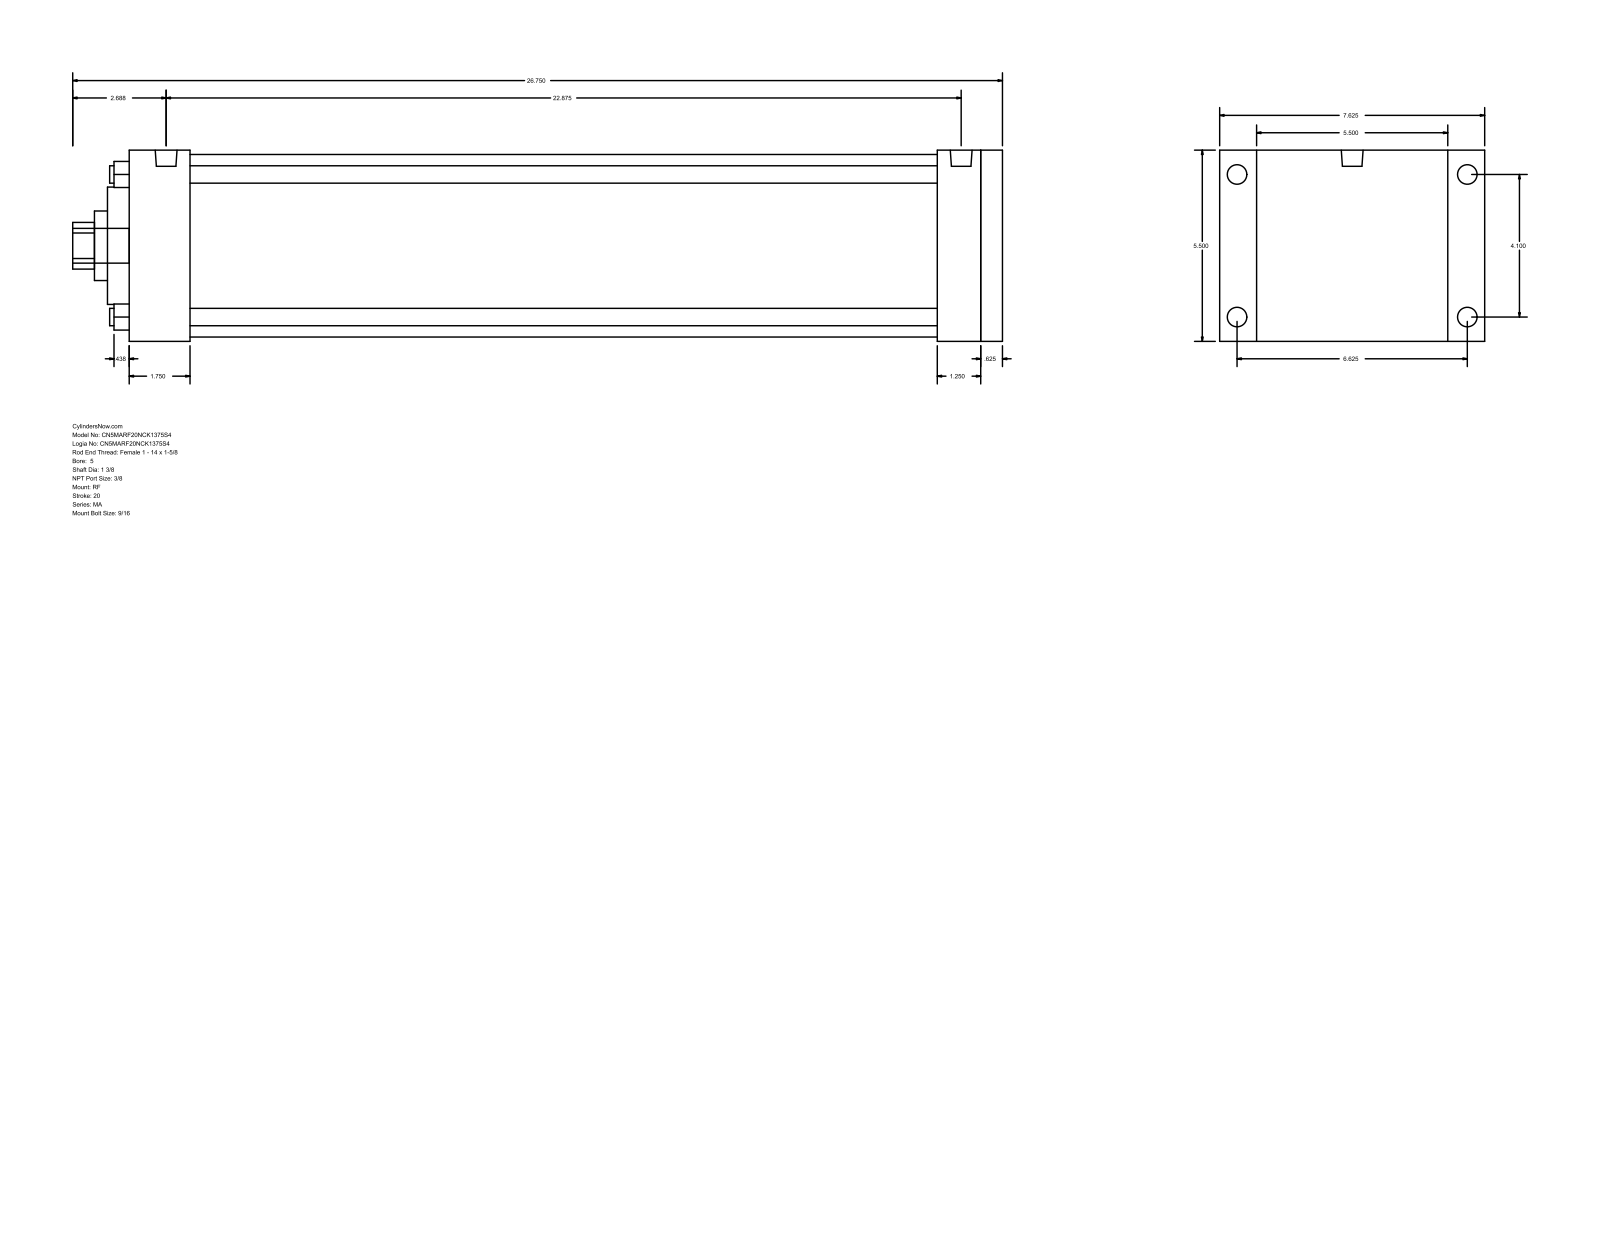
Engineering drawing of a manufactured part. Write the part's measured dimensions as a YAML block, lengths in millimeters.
part_name: "MA_RF__0500_1.375"
step_written_by: "GSSL Pune (CONFIG_CONTROL_DESIGN)"
units: millimeters
bodies: {solids: 0, faces: 94, planar: 65, cylindrical: 29, other: 0}
overall_size: [679.45, 193.68, 139.7]
round_holes:
  - {diameter: 12.7, count: 4}
  - {diameter: 34.92, count: 1}
  - {diameter: 50.8, count: 1}
  - {diameter: 85.72, count: 1}
  - {diameter: 133.35, count: 1}
round_bosses_or_shafts:
  - {diameter: 14.29, count: 4}
  - {diameter: 11.11, count: 4}
  - {diameter: 15.93, count: 2}
  - {diameter: 25.4, count: 1}
partial_cylinders:
  - {radius: 17.06, count: 1}
face_to_face_distances: [139.7, 638.18, 15.87, 622.31, 44.45, 577.86, 593.73, 590.56, 546.11, 31.75]
hole_center_spacings: [73.64, 104.14, 147.28]
